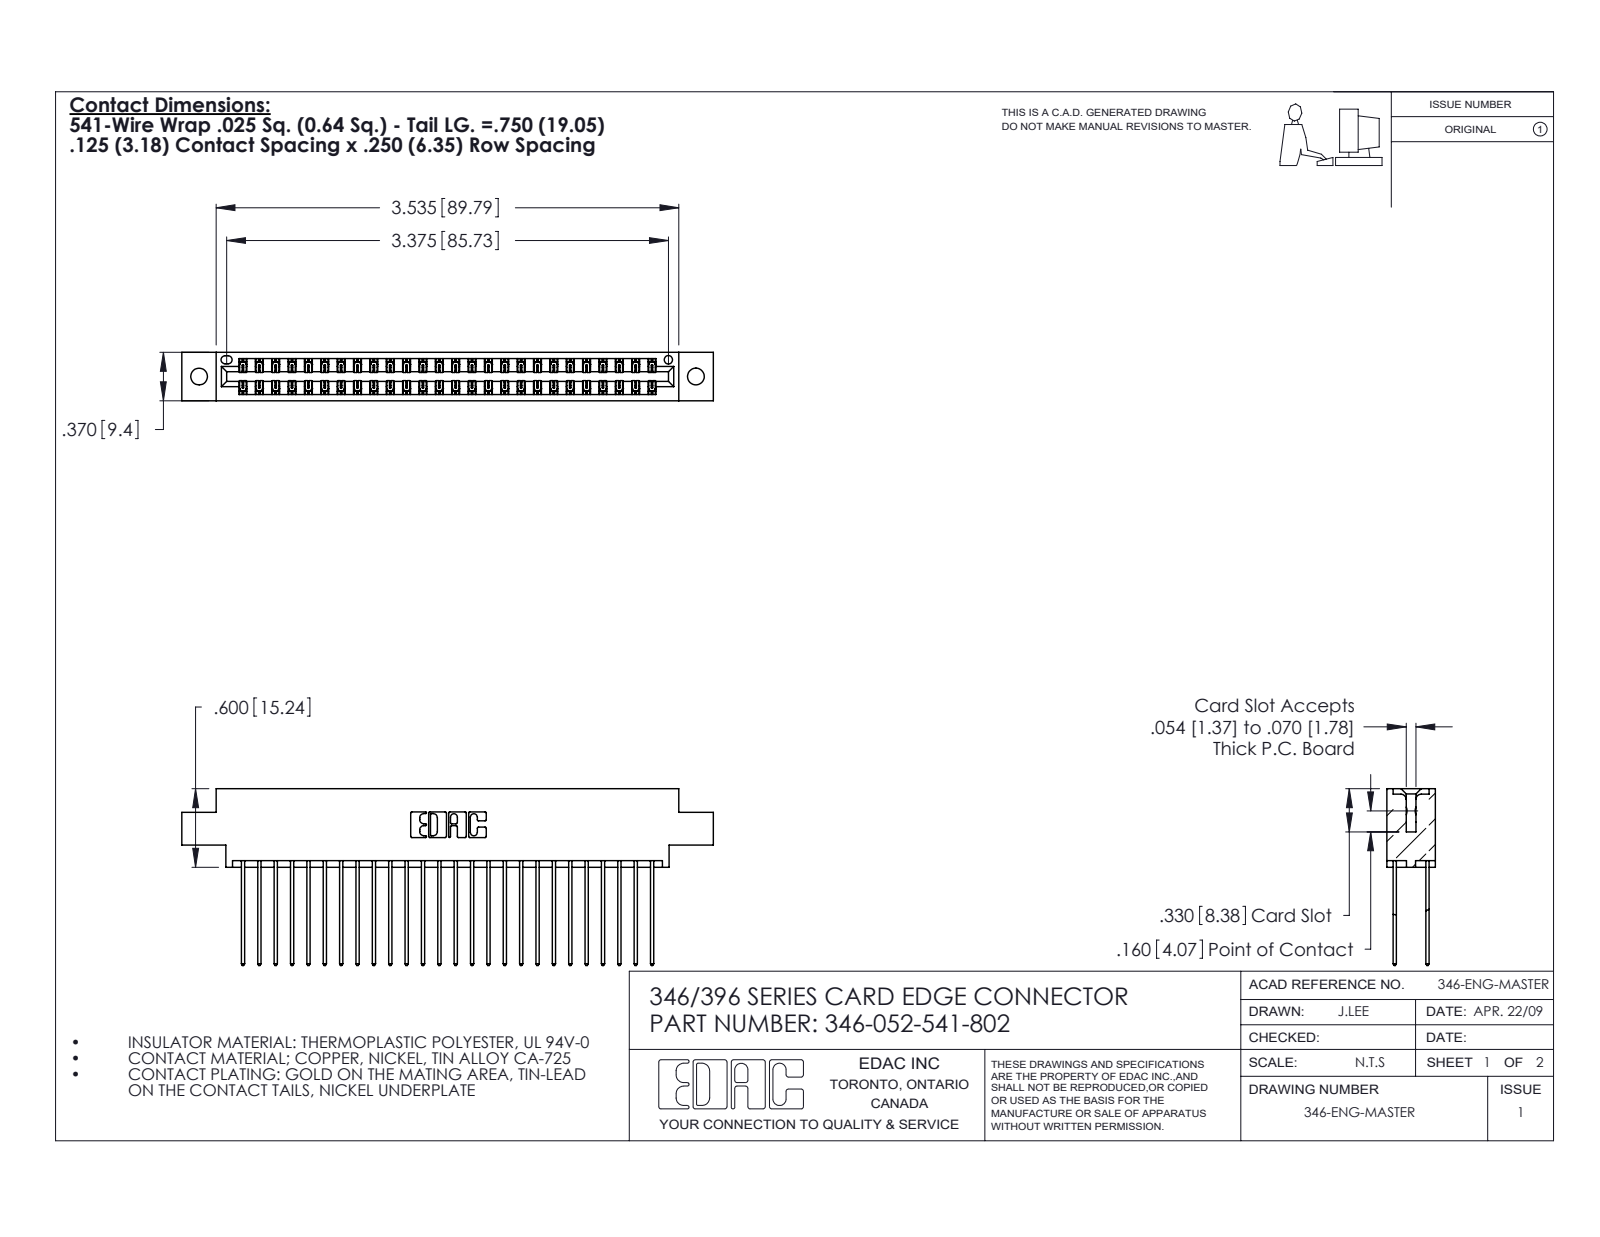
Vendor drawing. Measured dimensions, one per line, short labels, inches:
name: 345-292-001_345-293-141; 346 Part_0.170 Offset - 0.128 Dia; 346-052-541-802
written by: SolidWorks 2020 (CONFIG_CONTROL_DESIGN)
unit: in
bodies: 53 solids, 2830 faces (1900 planar, 930 cylindrical, 0 other)
size: 4.06 × 1.35 × 0.37
volume: 0.613 in³; area: 23.08 in²
holes: 2× ⌀0.128, 1× ⌀0.064
rounds: 78× R0.006, 52× R0.01, 22× R0.01, 6× R0.007, 6× R0.031, 3× R0.026, 2× R0.014, 2× R0.022
face distances: 0.048, 0.322, 0.25, 0.072, 0.298, 0.025, 0.37, 0.275, 0.225, 0.148
hole spacings: 0.246, 3.587, 3.795
